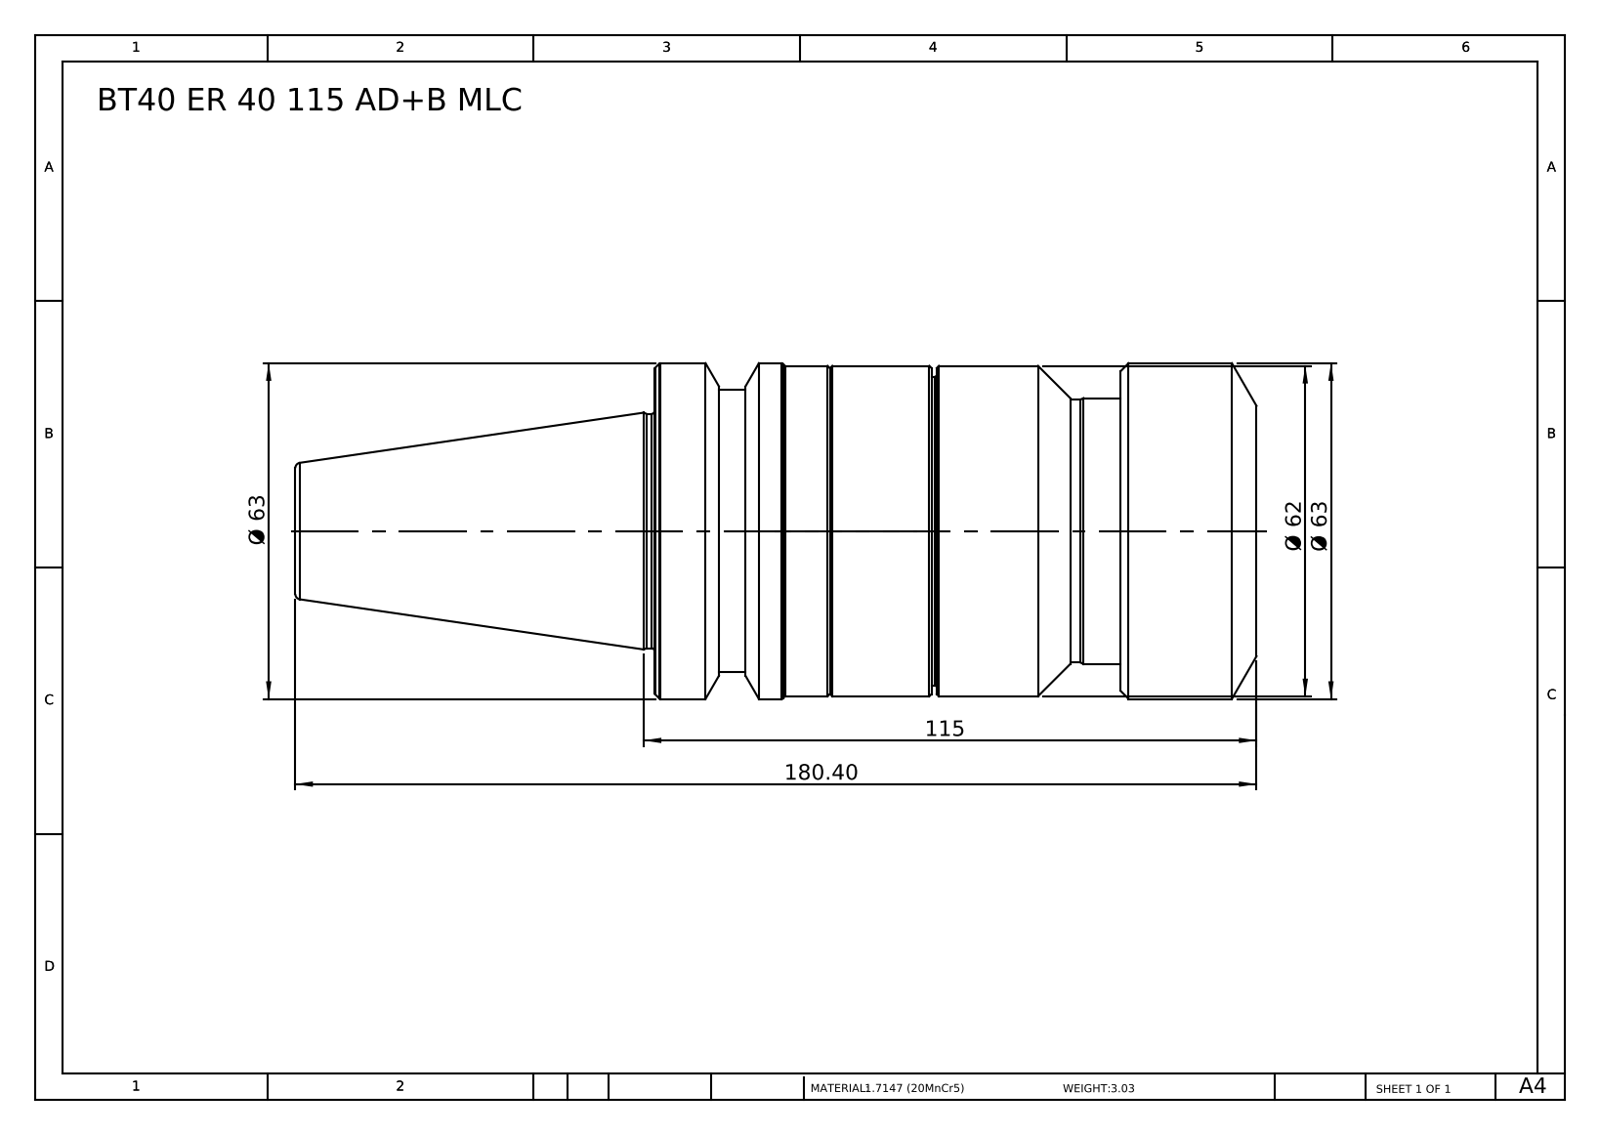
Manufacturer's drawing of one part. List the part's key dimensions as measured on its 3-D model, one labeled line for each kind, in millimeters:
Part name (STEP PRODUCT): BT40 ER 40 115 AD+B MLC
STEP written by: SolidWorks 2014 (CONFIG_CONTROL_DESIGN)
Units: millimetres
Bodies: 1 solid, 72 faces (10 planar, 22 cylindrical, 40 other)
Overall size (bounding box): 180.4 × 63 × 63
Volume: 389 063 mm³ · Surface area: 36 721 mm²
Round bosses / shafts (diameter × count): ⌀63 ×1, ⌀62 ×1, ⌀57.9 ×1, ⌀53 ×1, ⌀49.9 ×1, ⌀49.4 ×1, ⌀44 ×1
Main face-to-face distances: 113, 25.5, 87.5, 180.4, 154.9, 67.4, 61, 35.5, 52, 119.4
